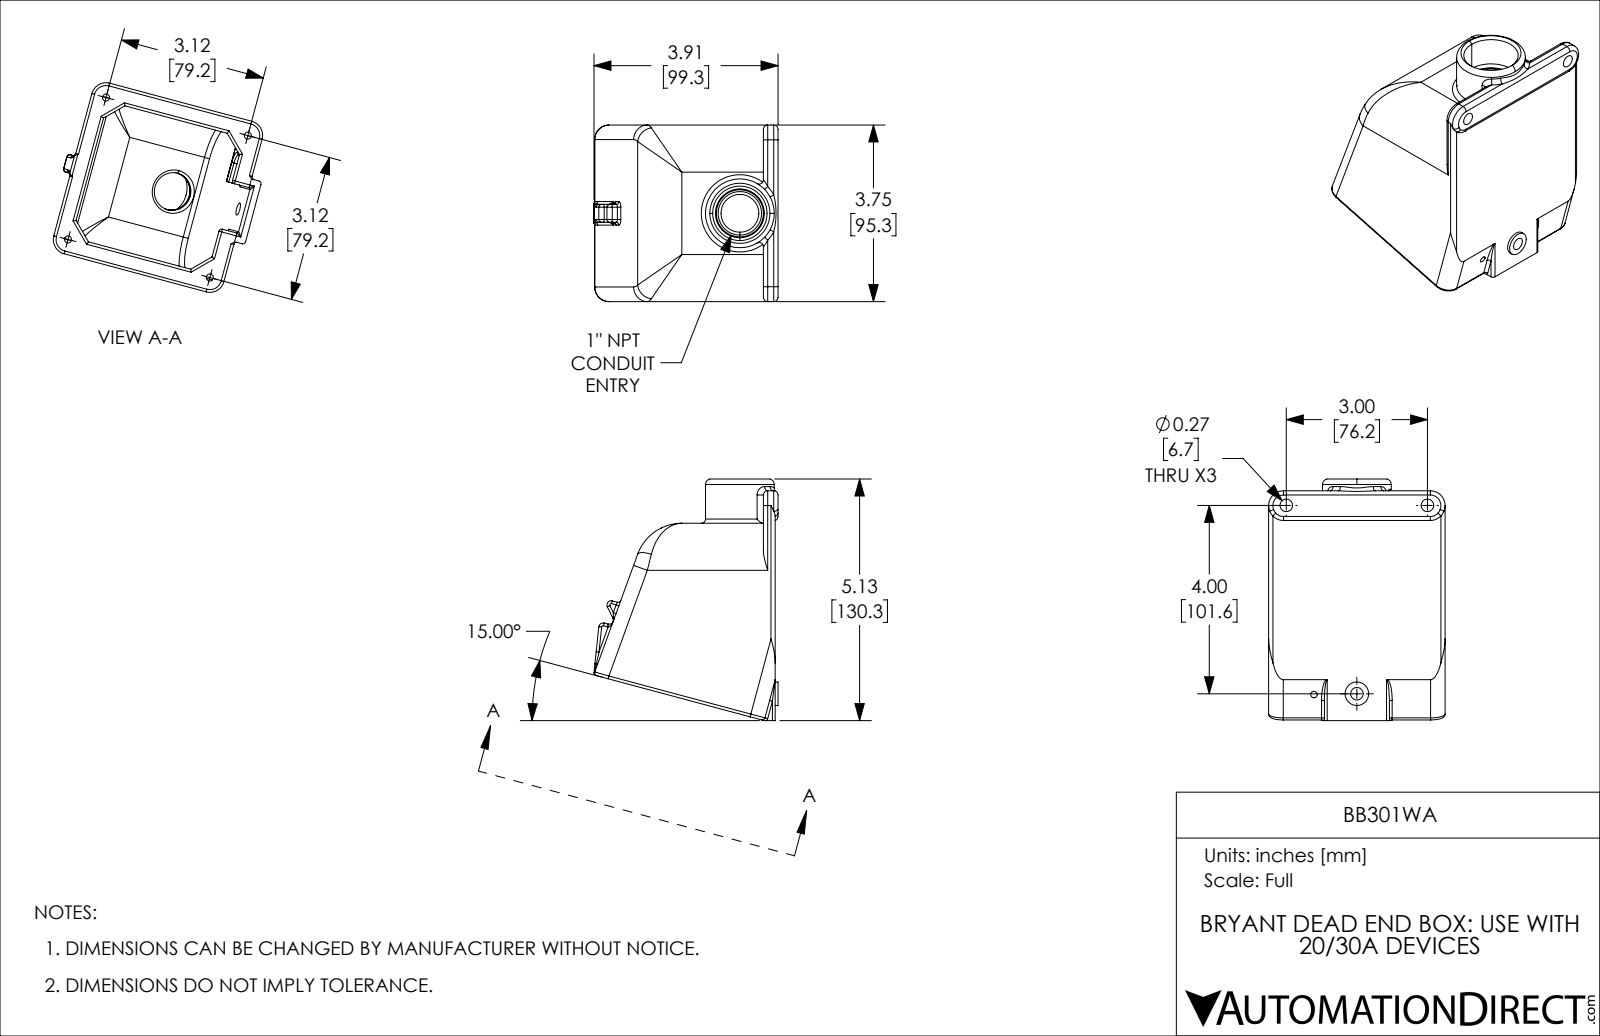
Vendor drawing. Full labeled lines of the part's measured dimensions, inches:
Part name (STEP PRODUCT): BB301WA
STEP written by: SolidWorks 2021 (CONFIG_CONTROL_DESIGN)
Units: inches
Bodies: 1 solid, 428 faces (63 planar, 244 cylindrical, 121 other)
Overall size (bounding box): 5.13 × 3.912 × 3.75
Volume: 12.41 in³ · Surface area: 128.6 in²
Round holes (diameter × count): ⌀0.15 ×4, ⌀0.265 ×2, ⌀0.136 ×1, ⌀0.265 ×1, ⌀0.803 ×1, ⌀1.12 ×1, ⌀1.156 ×1
Round bosses / shafts (diameter × count): ⌀1.46 ×1, ⌀0.5 ×1
Partial cylindrical surfaces — rounded edges, fillets, slot ends (radius × count): R0.06 ×59, R0.09 ×21, R0.12 ×4, R0.25 ×4, R0.31 ×4, R0.81 ×3, R1 ×3, R0.035 ×2
Main face-to-face distances: 0.19, 3.56, 3.37, 3.75, 0.25, 0.06, 0.03, 3.53, 3.72, 0.16
Hole centre spacings: 3.12, 3.12, 4.272, 4.412, 0.913, 3, 4.06, 4.686
